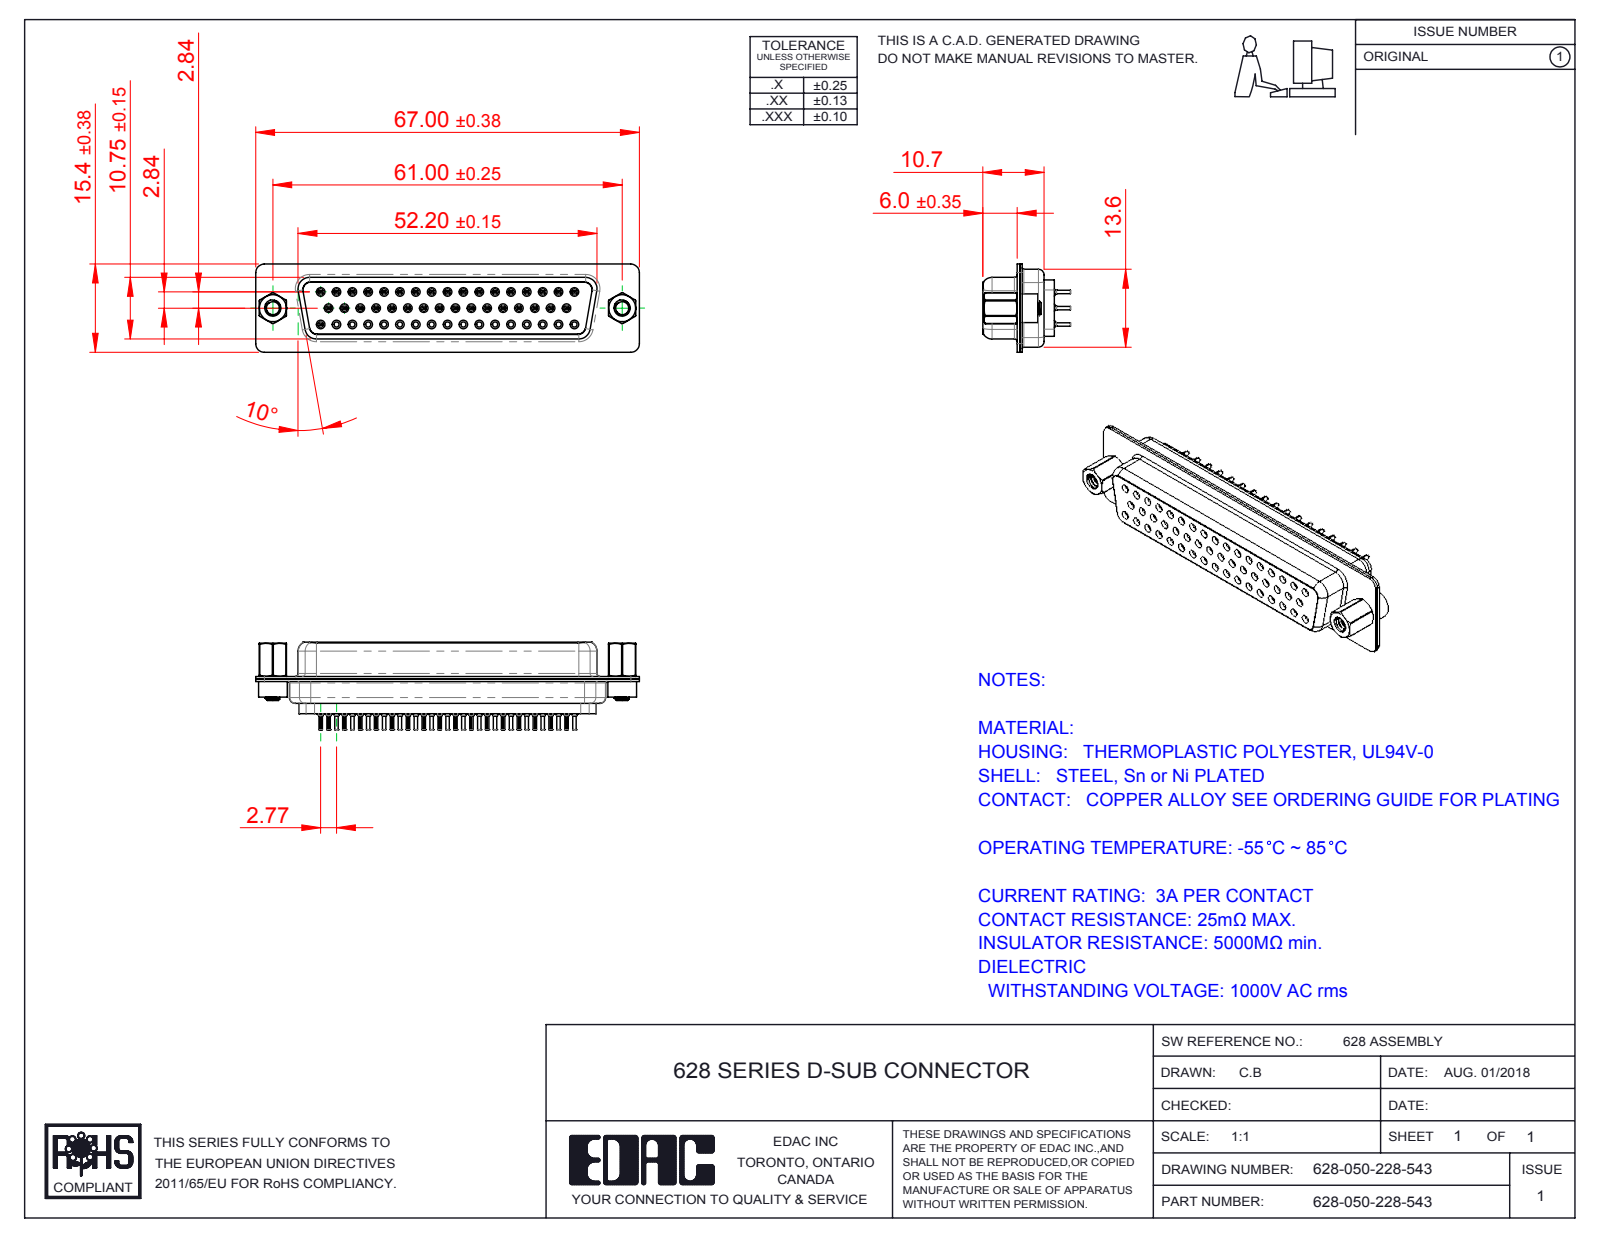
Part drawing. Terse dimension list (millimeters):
name: 628 Contact Row 1_28L; 628 4-40 Threaded Rivet; 628 4-40 Hex Standoff; 628 Housing_50 LP (+5 more)
written by: SolidWorks 2016 (CONFIG_CONTROL_DESIGN)
unit: mm
bodies: 41 solids, 4931 faces (1191 planar, 1459 cylindrical, 2281 other)
size: 67 × 15.4 × 15.3
volume: 6 795 mm³; area: 14 085 mm²
holes: 50× ⌀0.9, 50× ⌀1.6, 34× ⌀0.2, 34× ⌀0.8, 34× ⌀1.1, 17× ⌀1.7, 16× ⌀1.5, 16× ⌀2, 2× ⌀2.26, 2× ⌀2.29, 2× ⌀4, 2× ⌀4.8
bosses: 34× ⌀2, 34× ⌀1.5, 34× ⌀1.2, 34× ⌀0.6, 2× ⌀5, 2× ⌀4.9, 2× ⌀2.79
rounds: 68× R0.1, 33× R0.28, 16× R1.5, 12× R2, 8× R1.35, 4× R0.25, 4× R0.5, 4× R0.6
face distances: 0.45, 0.4, 10.3, 0.9, 6.05, 6.5, 6, 6.45, 12.5, 11.33
hole spacings: 3.16, 2.77, 5.54, 8.31, 11.08, 13.85, 16.62, 19.39
